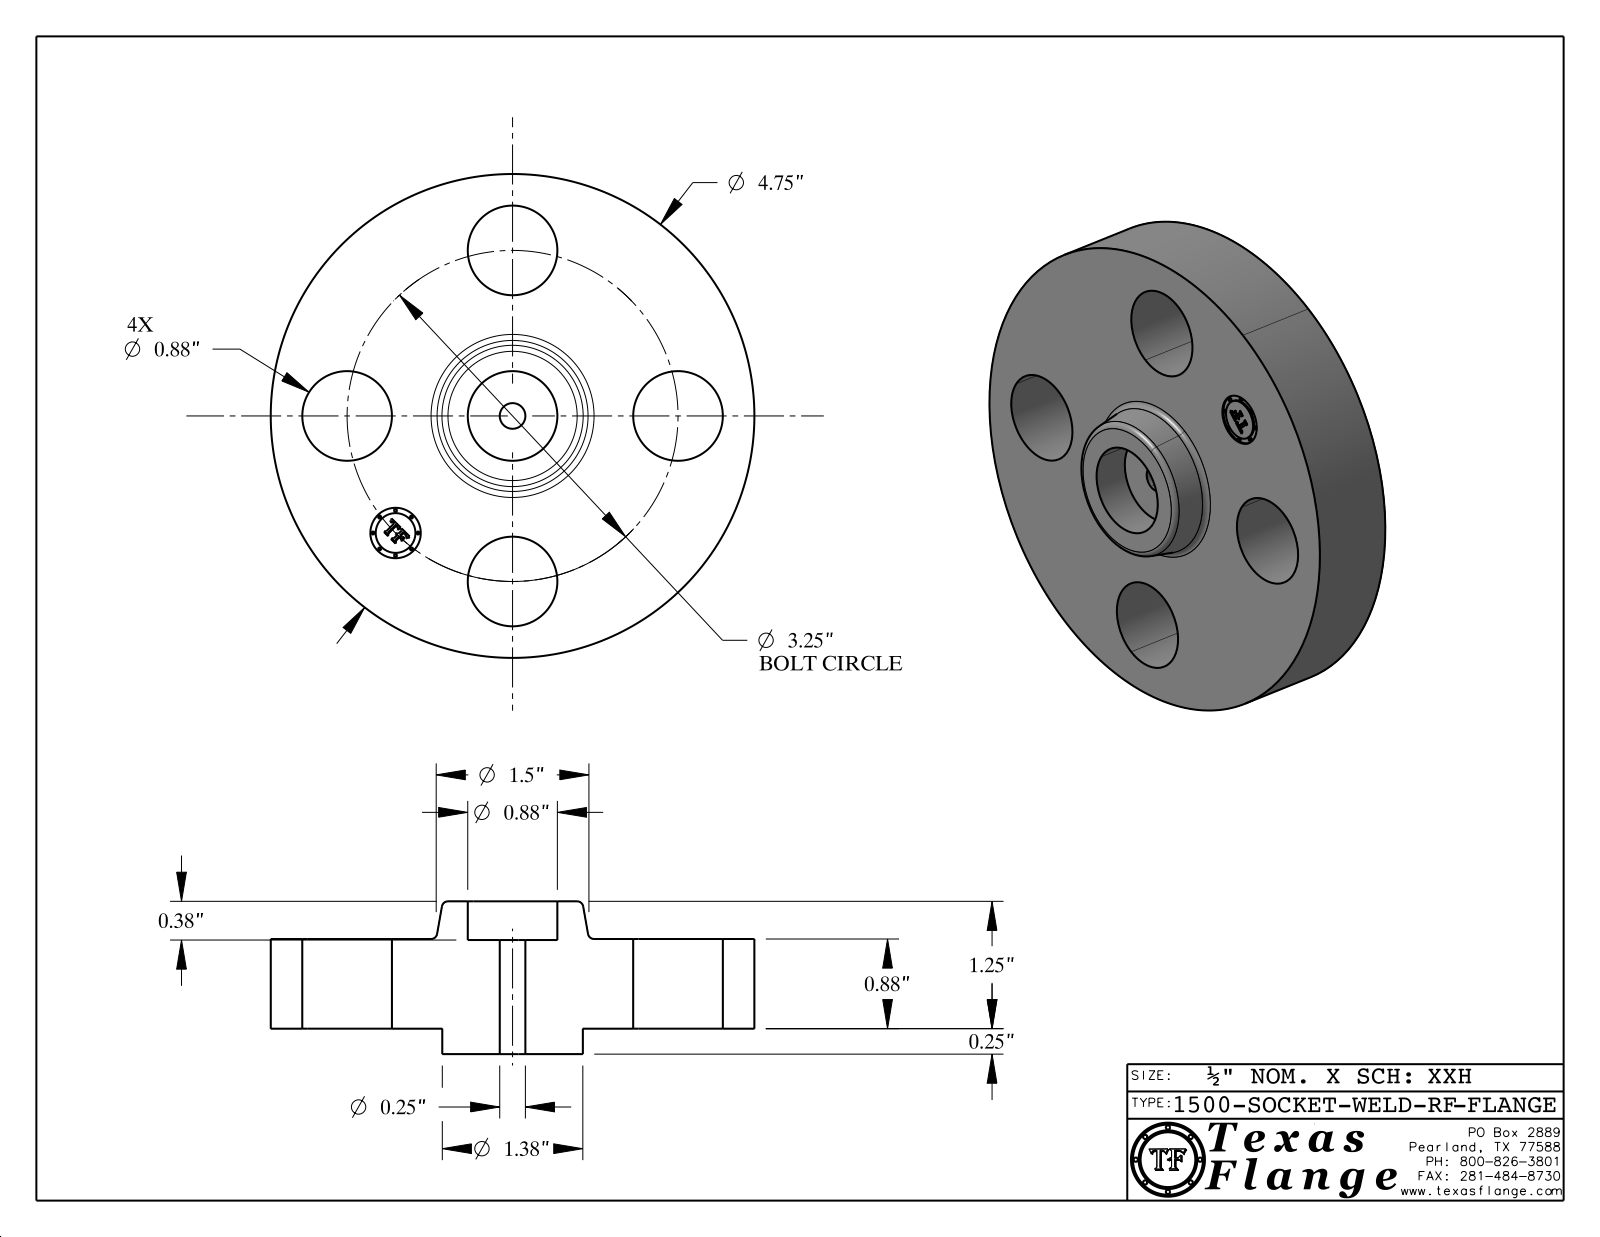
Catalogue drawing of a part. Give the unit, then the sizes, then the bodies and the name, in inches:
Units: inches
Overall size (bounding box): 4.75 × 4.75 × 1.5
Round holes (diameter × count): ⌀0.88 ×5, ⌀0.252 ×1, ⌀0.495 ×1
Round bosses / shafts (diameter × count): ⌀0.03 ×8, ⌀4.75 ×1, ⌀1.38 ×1, ⌀0.39 ×1
Main face-to-face distances: 0.88, 0.25, 1.13, 1.5, 1.25, 0.37, 1.12, 0.87, 0.38, 1.115
Hole centre spacings: 1.625, 2.298, 1.244, 3.003, 3.25
Volume: 14.14 in³ · Surface area: 57.7 in²
Bodies: 1 solid, 412 faces (370 planar, 36 cylindrical, 6 other)
Part name (STEP PRODUCT): 1500-SOCKET-WELD-RF
STEP written by: CATIA V5 STEP AP214 (AUTOMOTIVE_DESIGN)
